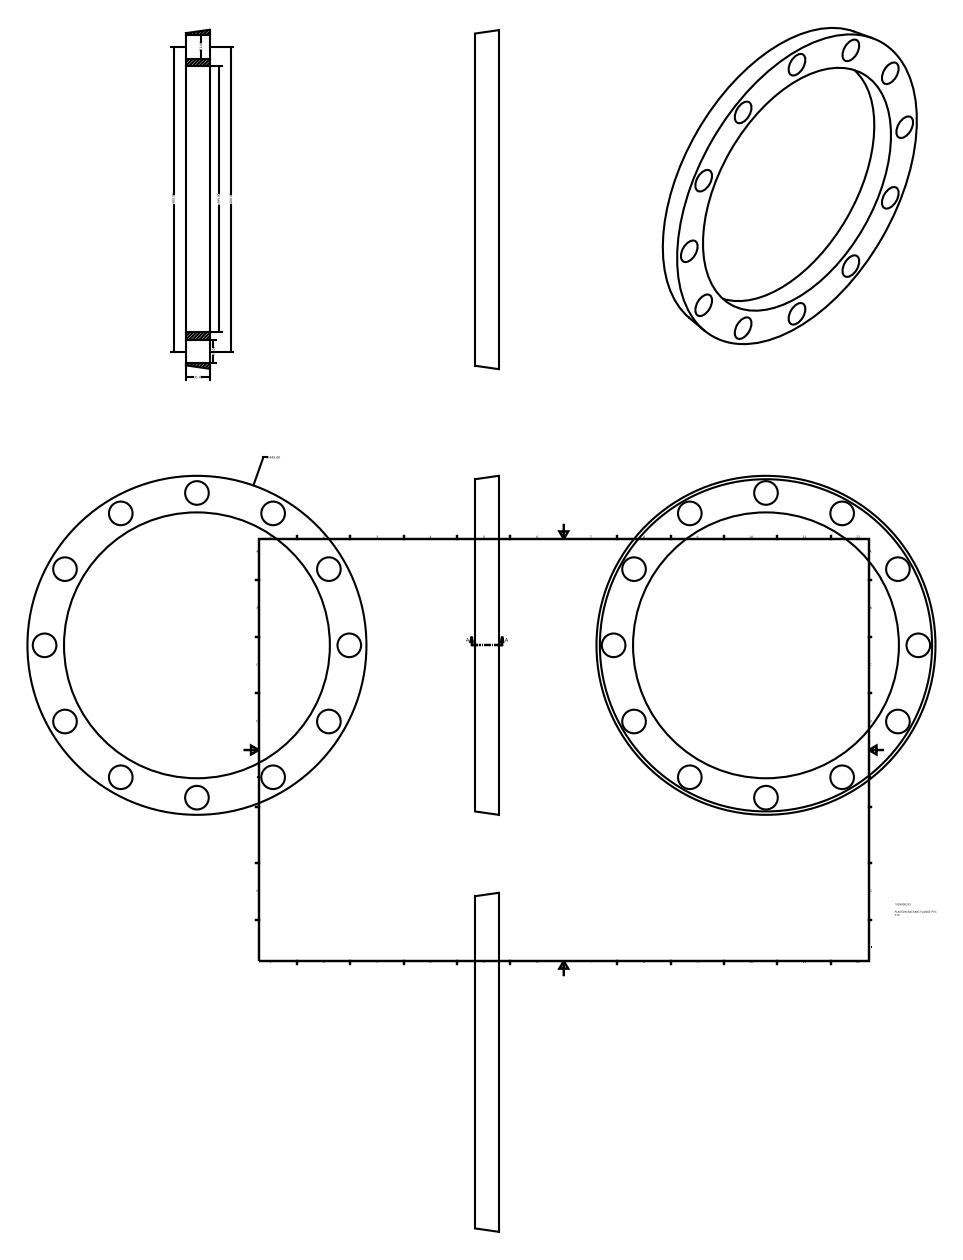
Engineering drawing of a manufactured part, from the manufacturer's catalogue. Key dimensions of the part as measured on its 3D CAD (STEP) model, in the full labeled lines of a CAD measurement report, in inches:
Part name (STEP PRODUCT): (_AS)059000315
STEP written by: Autodesk Inventor 2015 (AUTOMOTIVE_DESIGN)
Units: inches
Bodies: 1 solid, 16 faces (2 planar, 13 cylindrical, 1 other)
Overall size (bounding box): 17.52 × 17.52 × 1.22
Volume: 90.25 in³ · Surface area: 324 in²
Round holes (diameter × count): ⌀1.22 ×12, ⌀13.74 ×1
Main face-to-face distances: 1.22
Hole centre spacings: 7.874, 4.076, 15.212, 11.136, 13.638, 11.135, 13.639, 15.748
